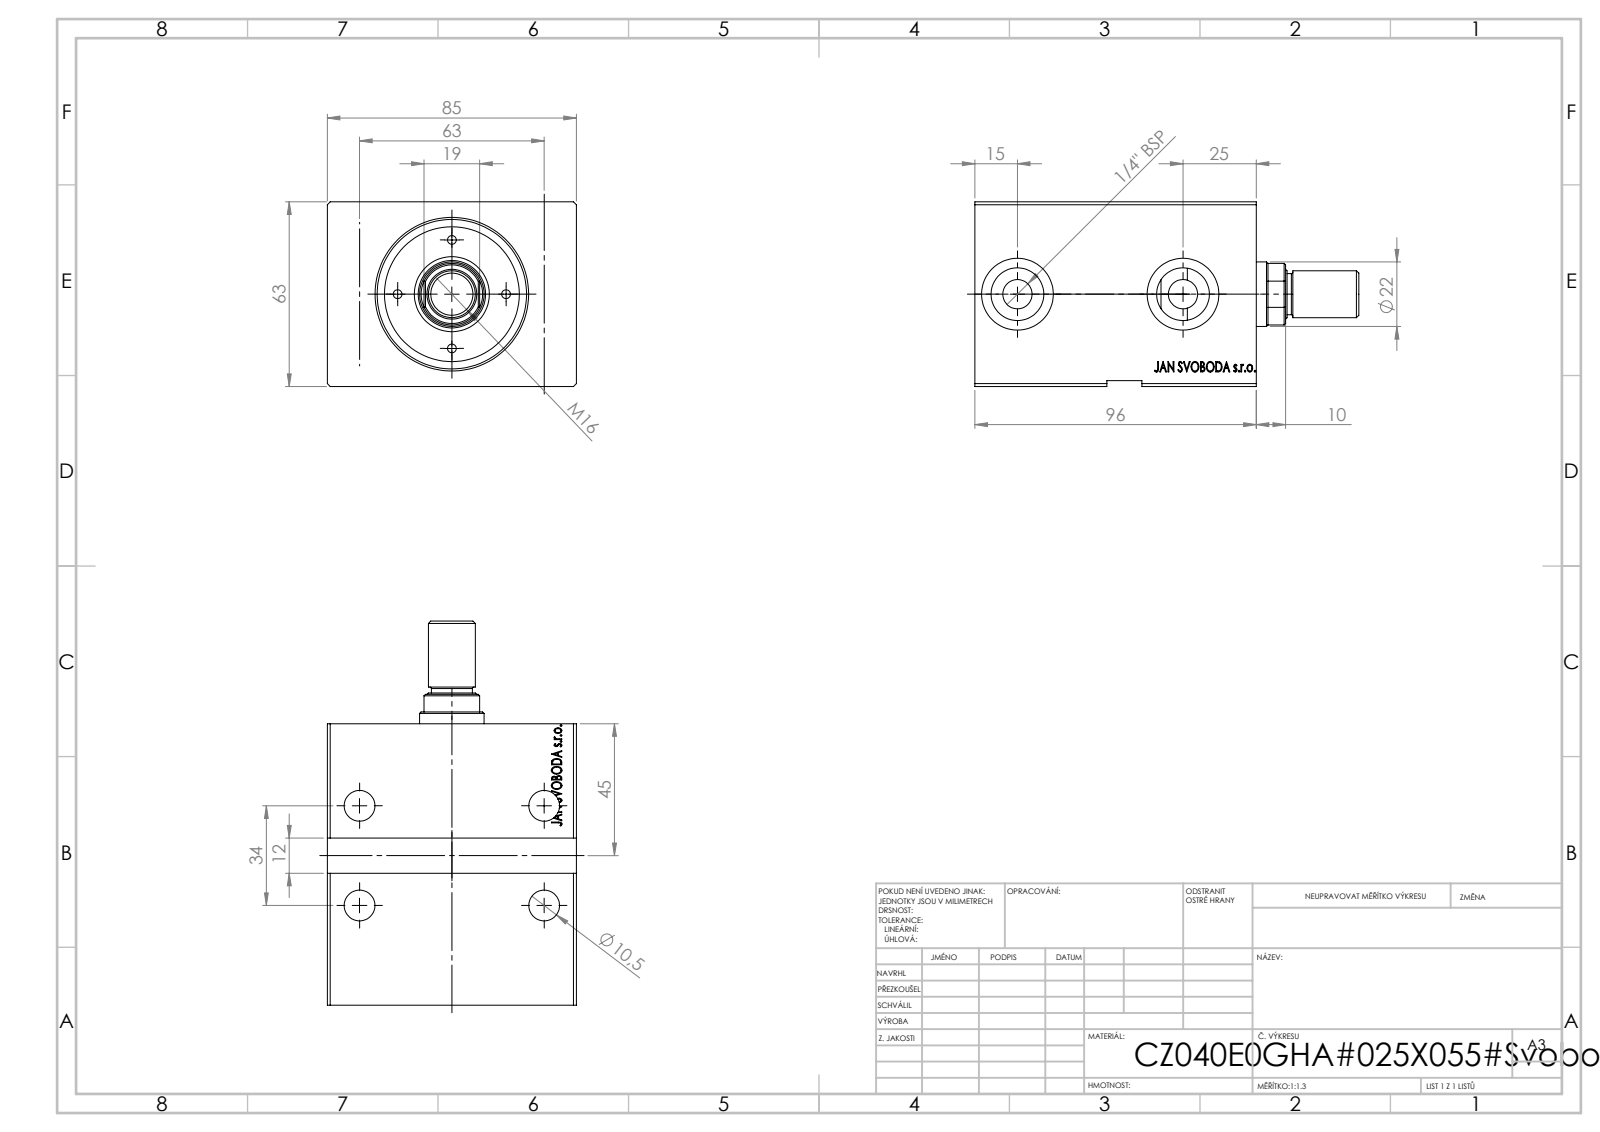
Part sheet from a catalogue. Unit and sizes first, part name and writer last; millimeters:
Units: millimetres
Overall size (bounding box): 96 × 85 × 63
Round holes (diameter × count): ⌀10.5 ×4, ⌀8 ×2, ⌀10 ×2, ⌀18 ×2, ⌀24.5 ×2, ⌀36 ×1, ⌀40 ×1, ⌀51 ×1
Main face-to-face distances: 63, 85, 96, 80.7, 15.3, 2, 61, 95.8, 15.1, 10
Hole centre spacings: 34, 63, 71.59, 18.85, 19.91, 32.18, 36.5, 46.04
Volume: 373 446 mm³ · Surface area: 58 790 mm²
Bodies: 1 solid, 781 faces (384 planar, 31 cylindrical, 366 other)
STEP written by: SolidWorks 2019 (CONFIG_CONTROL_DESIGN)
